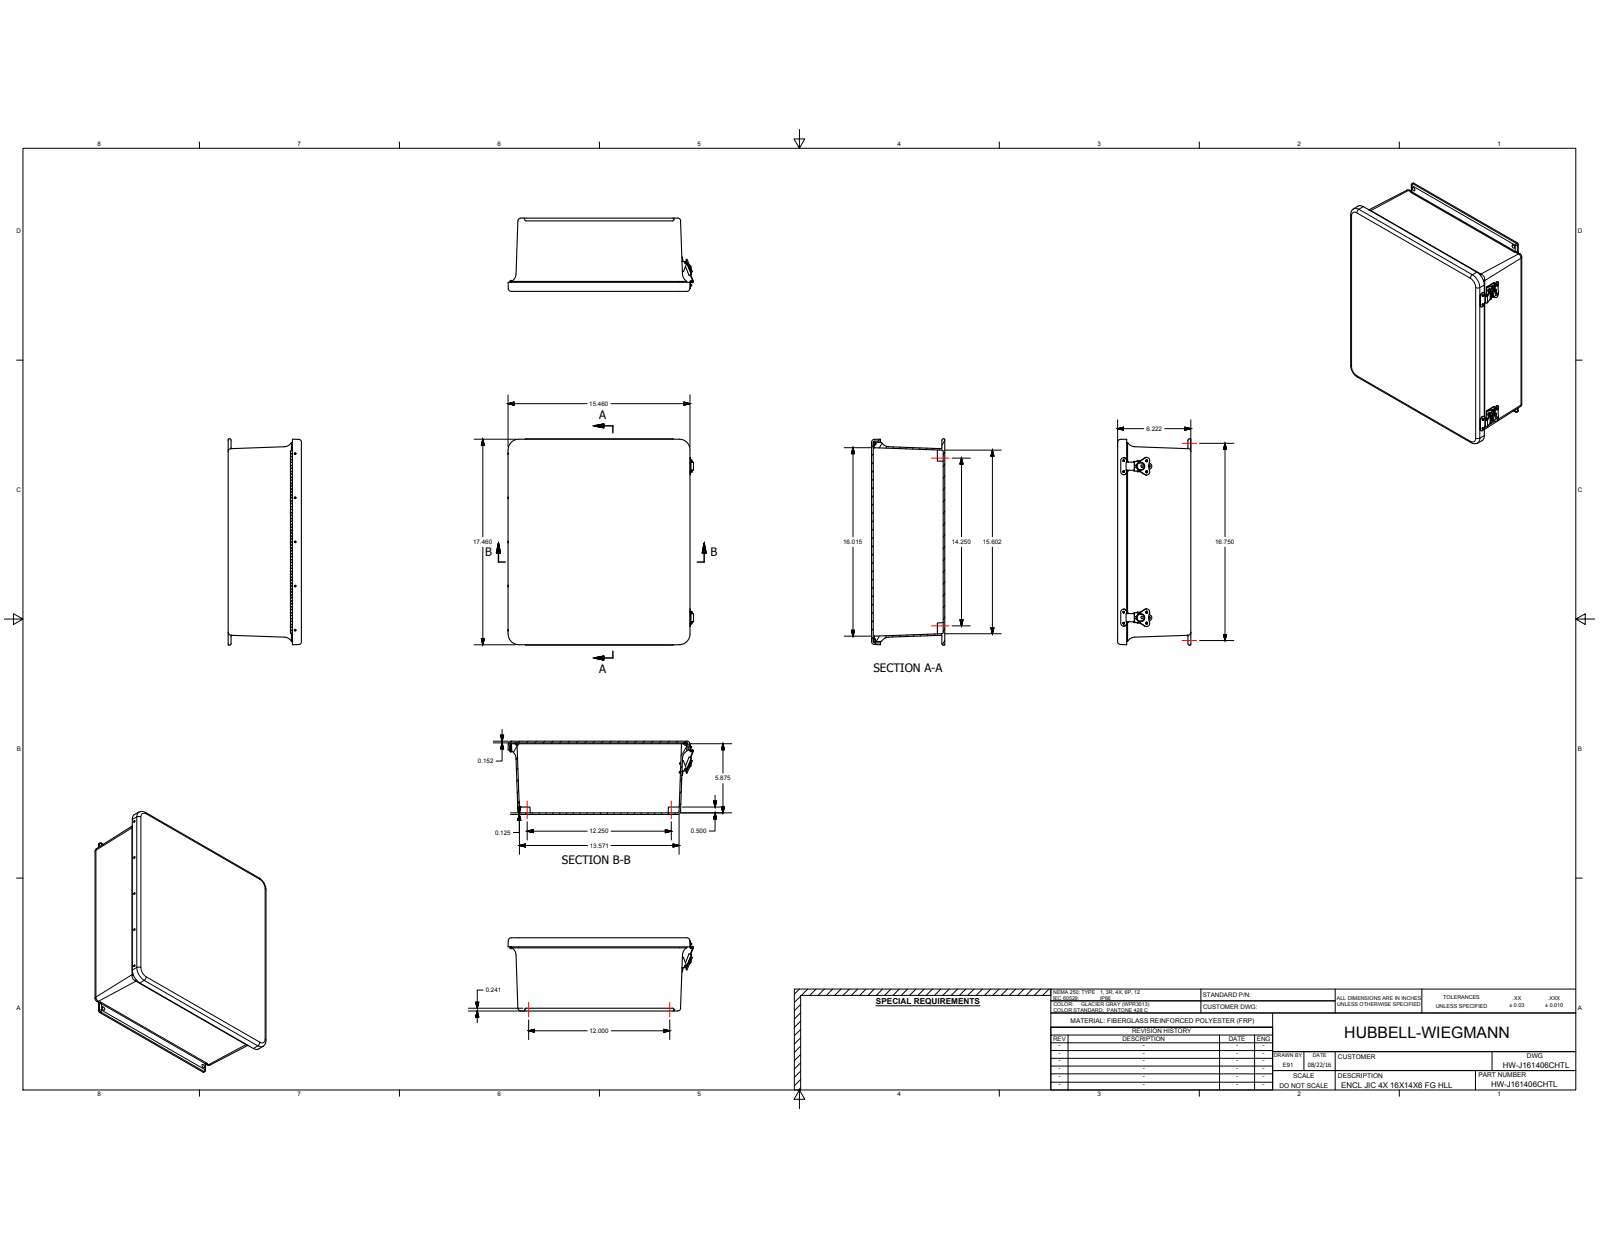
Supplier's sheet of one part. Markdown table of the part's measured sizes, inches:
| quantity | value |
| --- | --- |
| part name | HW-J1614CHTL; WP1614HLU; WP1614HLCVR; RMGAS_WP1614HCVR (+8 more) |
| STEP written by | Autodesk Inventor 2017 (AUTOMOTIVE_DESIGN) |
| units | inches |
| bodies | 44 solids, 1090 faces (527 planar, 445 cylindrical, 118 other) |
| overall size | 17.53 × 15.741 × 6.222 |
| volume | 144.4 in³ |
| surface area | 1 973 in² |
| round holes (diameter × count) | 0.14 × 20, 0.104 × 18, 0.131 × 10, 0.152 × 8, 0.13 × 4, 0.133 × 4, 0.187 × 4, 0.218 × 4, 0.312 × 4, 0.135 × 2, 0.189 × 2, 0.191 × 2 |
| round bosses / shafts (diameter × count) | 0.125 × 18, 0.66 × 2, 0.582 × 2, 0.525 × 2, 0.286 × 2, 0.213 × 2, 0.18 × 2, 0.125 × 2 |
| partial cylindrical surfaces (radius × count) | 0.125 × 17, 0.015 × 16, 0.06 × 13, 0.25 × 10, 0.011 × 8, 0.02 × 8, 0.055 × 8, 0.07 × 8 |
| main face-to-face distances | 0.125, 0.152, 6.222, 6.07, 6.097, 5.944, 0.125, 0.222, 0.07, 5.875 |
| hole center spacings | 3.75, 7.5, 11.25, 12.868, 12.869, 0.25, 3.25, 3.5 |
